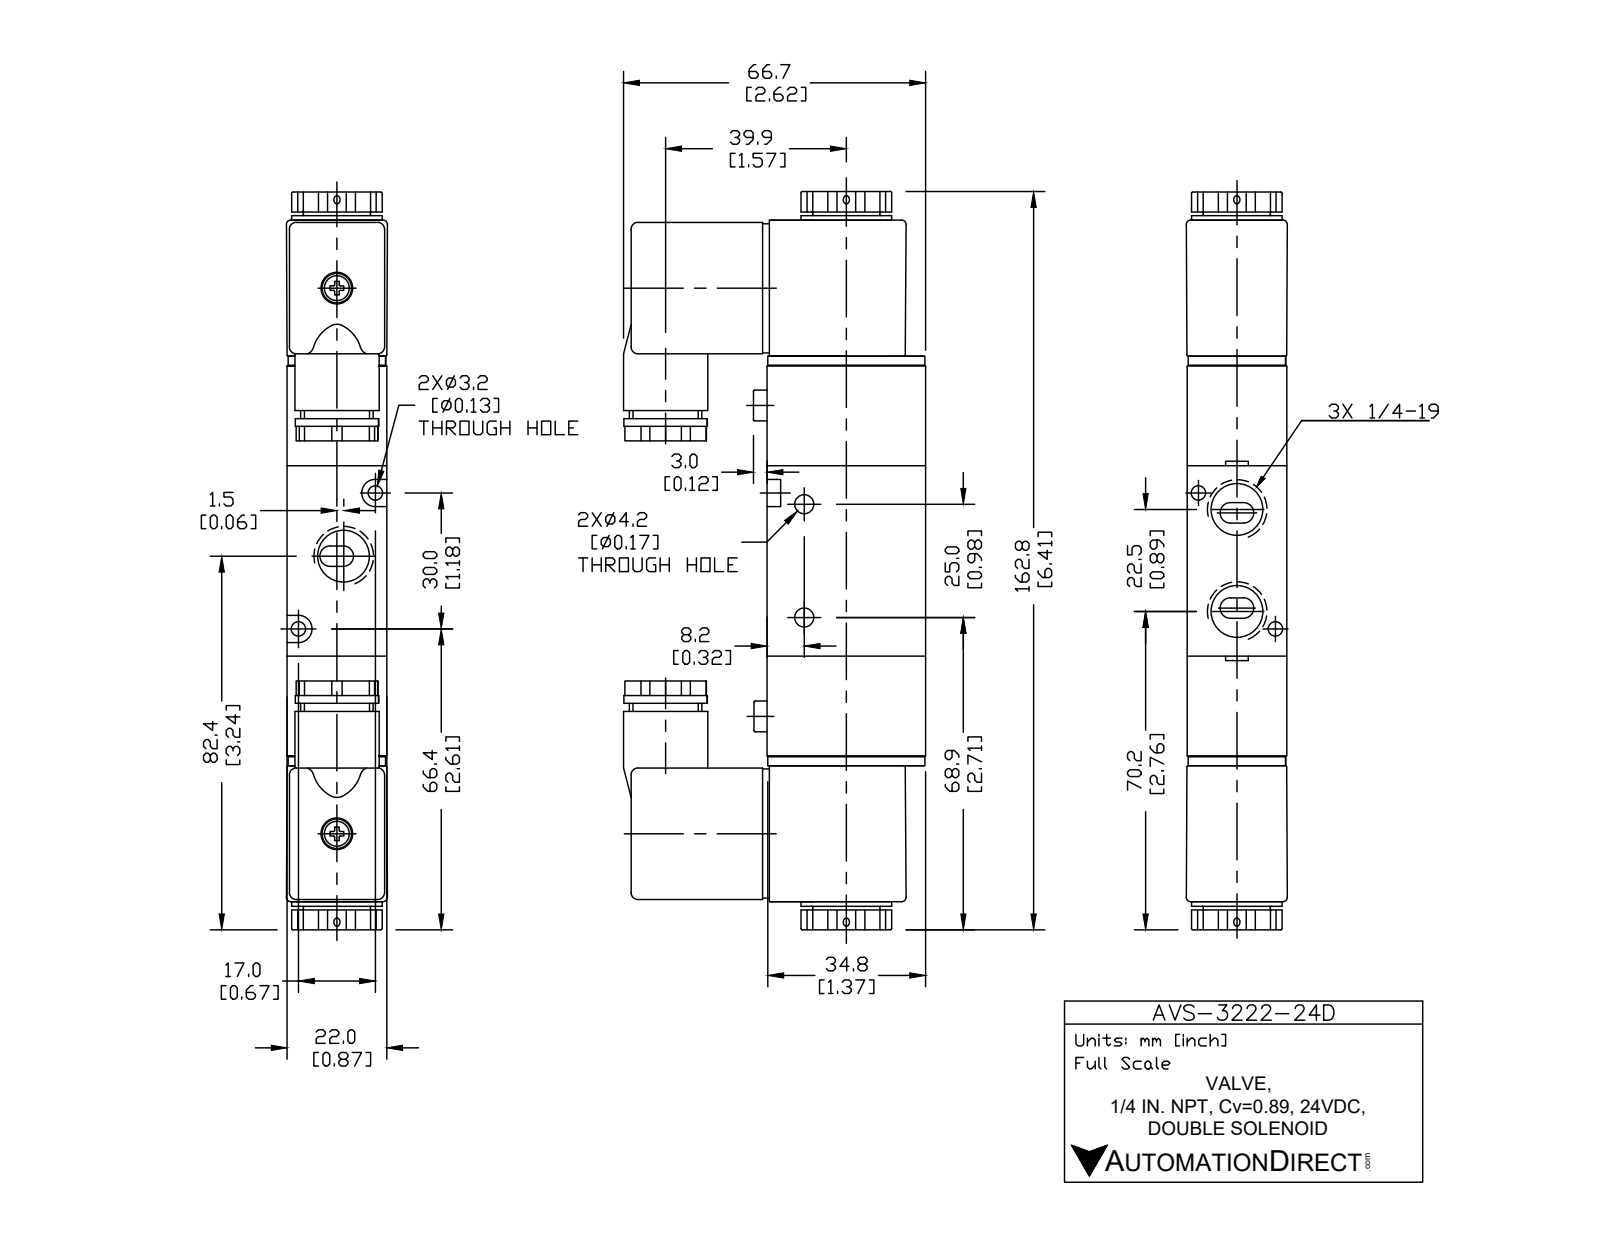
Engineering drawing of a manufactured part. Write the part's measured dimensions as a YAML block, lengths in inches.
part_name: "AVS-3222-24D"
step_written_by: "SolidWorks 2015 (CONFIG_CONTROL_DESIGN)"
units: inches
bodies: {solids: 5, faces: 252, planar: 138, cylindrical: 82, other: 32}
overall_size: [6.409, 2.626, 0.866]
volume: 9.209
surface_area: 53.46
round_holes:
  - {diameter: 0.438, count: 3}
  - {diameter: 0.13, count: 2}
  - {diameter: 0.169, count: 2}
  - {diameter: 0.366, count: 1}
round_bosses_or_shafts:
  - {diameter: 0.268, count: 2}
  - {diameter: 0.787, count: 1}
  - {diameter: 0.732, count: 1}
  - {diameter: 0.724, count: 1}
  - {diameter: 0.63, count: 1}
  - {diameter: 0.583, count: 1}
partial_cylinders:
  - {radius: 0.039, count: 20}
  - {radius: 0.02, count: 12}
  - {radius: 0.118, count: 2}
face_to_face_distances: [0.02, 0.89, 0.846, 0.827, 1.654, 0.898, 0.881, 0.866, 2.114, 3.768]
hole_center_spacings: [0.365, 0.367, 0.41, 0.484, 0.616, 0.743, 0.886, 0.984]
